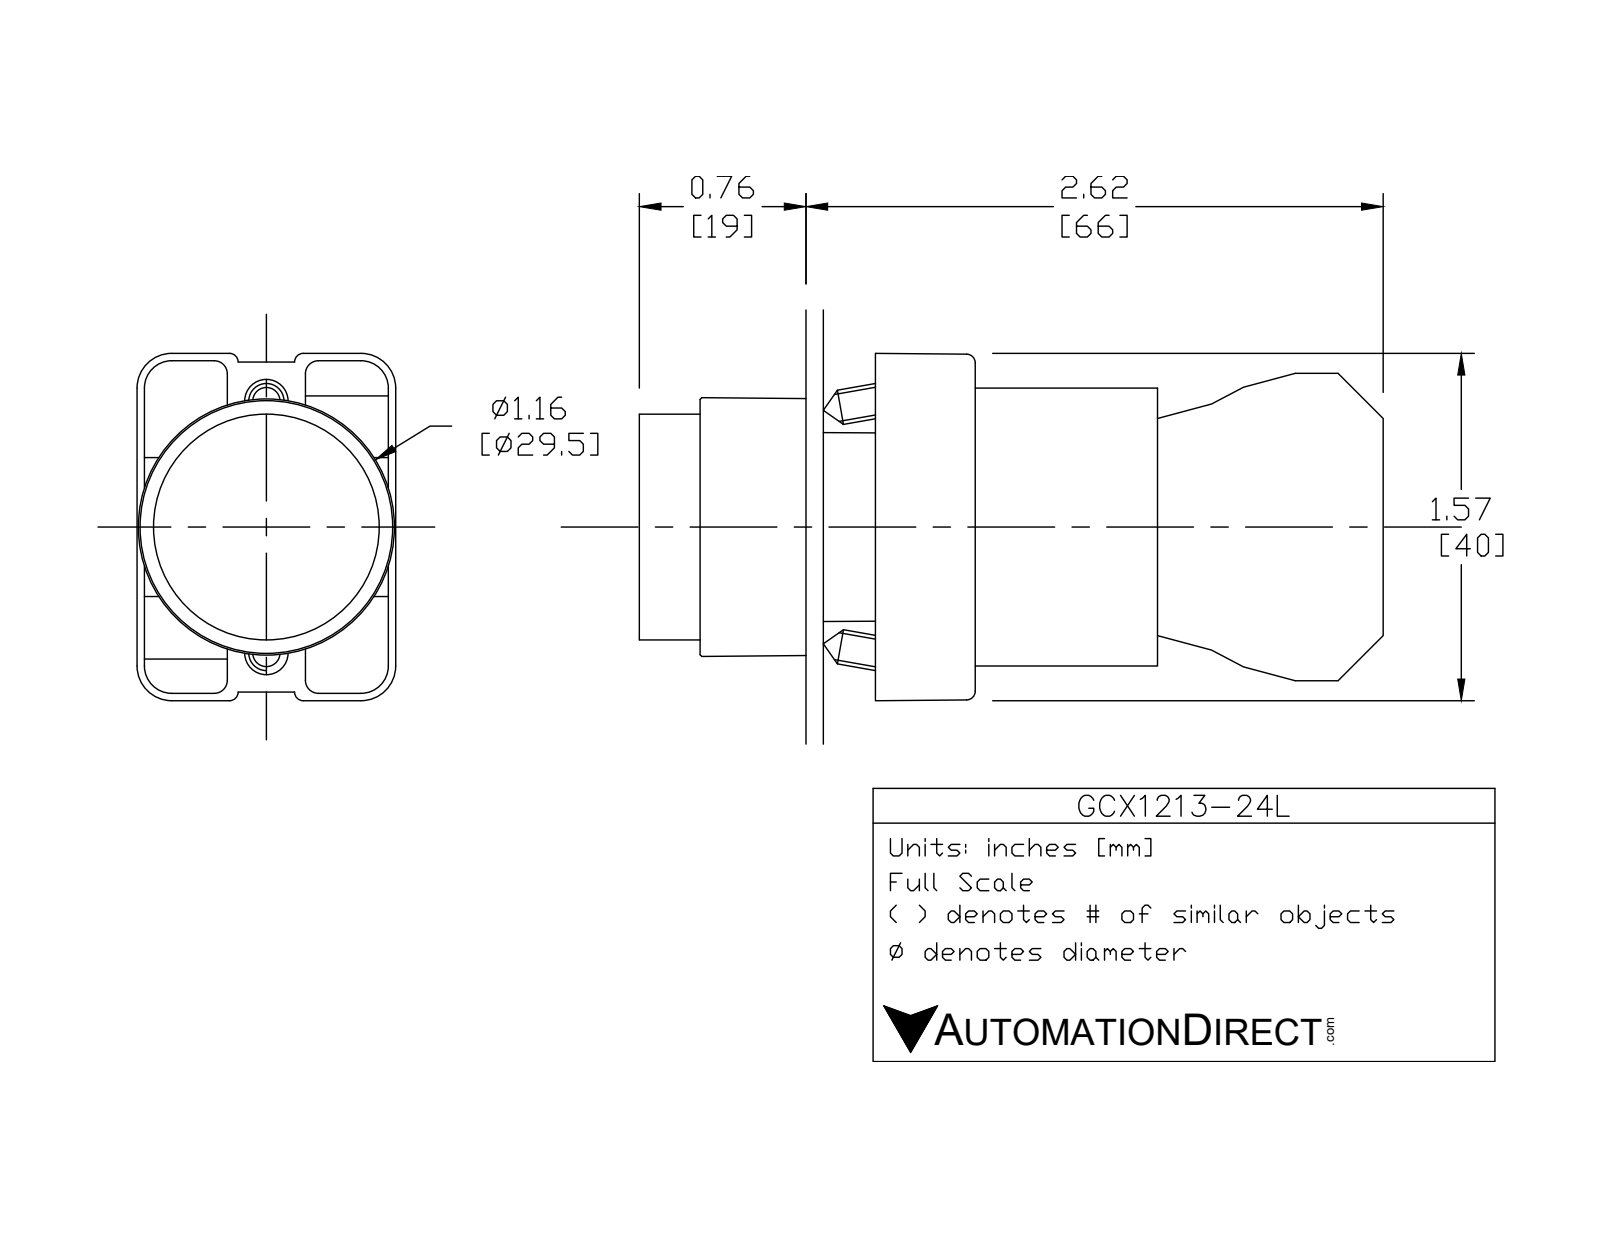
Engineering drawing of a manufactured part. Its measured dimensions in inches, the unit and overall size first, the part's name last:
Units: inches
Overall size (bounding box): 3.319 × 1.581 × 1.177
Round holes (diameter × count): ⌀0.079 ×2, ⌀0.124 ×2, ⌀0.13 ×2, ⌀0.087 ×1, ⌀0.197 ×1, ⌀0.469 ×1, ⌀0.878 ×1, ⌀0.888 ×1, ⌀1.024 ×1
Round bosses / shafts (diameter × count): ⌀0.157 ×4, ⌀1.175 ×1, ⌀1.004 ×1, ⌀0.945 ×1, ⌀0.856 ×1, ⌀0.78 ×1, ⌀0.504 ×1
Partial cylindrical surfaces — rounded edges, fillets, slot ends (radius × count): R0.059 ×24, R0.041 ×12, R0.124 ×12, R0.157 ×12, R0.039 ×8, R0.128 ×2, R0.02 ×1, R0.063 ×1
Main face-to-face distances: 0.827, 0.579, 1.171, 2.02, 1.193, 0.031, 0.033, 0.573, 1.165, 0.593
Hole centre spacings: 0.236, 0.544, 0.472, 0.49
Volume: 2.721 in³ · Surface area: 36.32 in²
Bodies: 7 solids, 425 faces (250 planar, 144 cylindrical, 31 other)
Part name (STEP PRODUCT): GCX1213L OPERATOR; ECX1050; ecx1040; ecx1029 (+1 more)
STEP written by: SolidWorks 2016 (AUTOMOTIVE_DESIGN)
